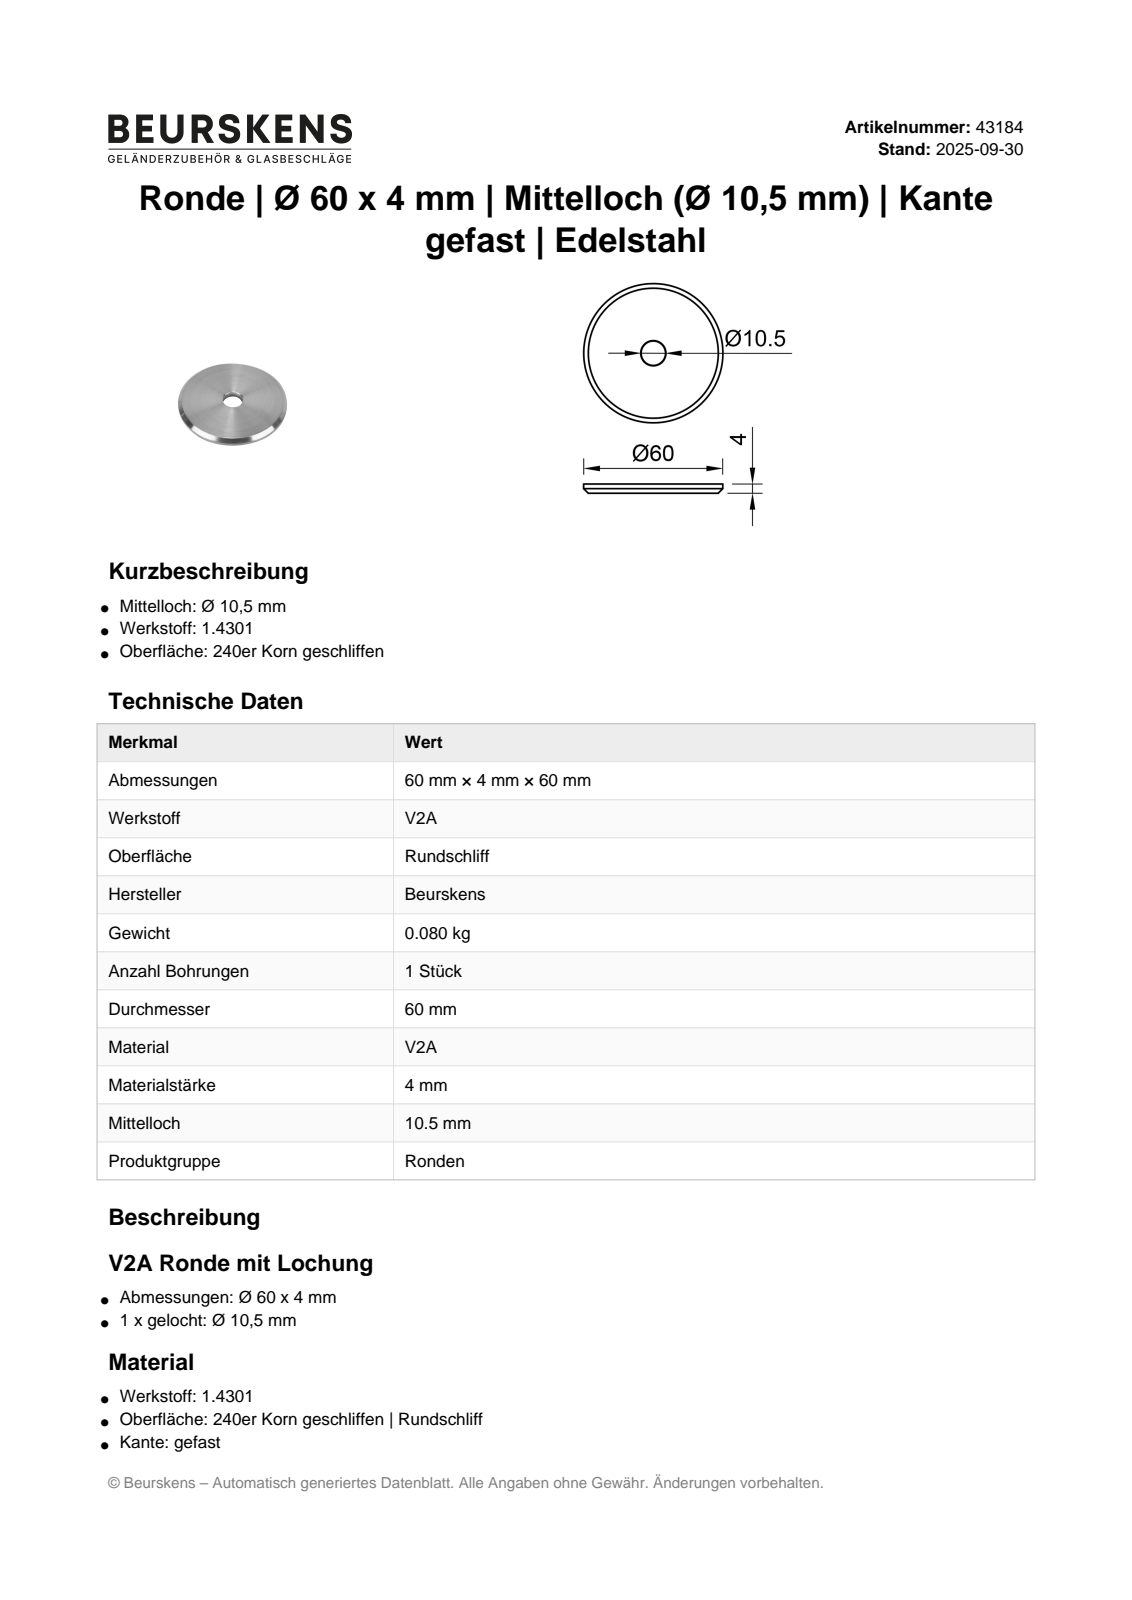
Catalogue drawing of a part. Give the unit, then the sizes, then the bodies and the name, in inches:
Units: inches
Overall size (bounding box): 2.362 × 2.362 × 0.157
Round holes (diameter × count): ⌀0.413 ×1
Round bosses / shafts (diameter × count): ⌀2.362 ×1
Main face-to-face distances: 0.157
Volume: 0.646 in³ · Surface area: 9.514 in²
Bodies: 1 solid, 6 faces (2 planar, 2 cylindrical, 2 other)
Part name (STEP PRODUCT): 43184
STEP written by: Autodesk Inventor 2022 (AUTOMOTIVE_DESIGN)
